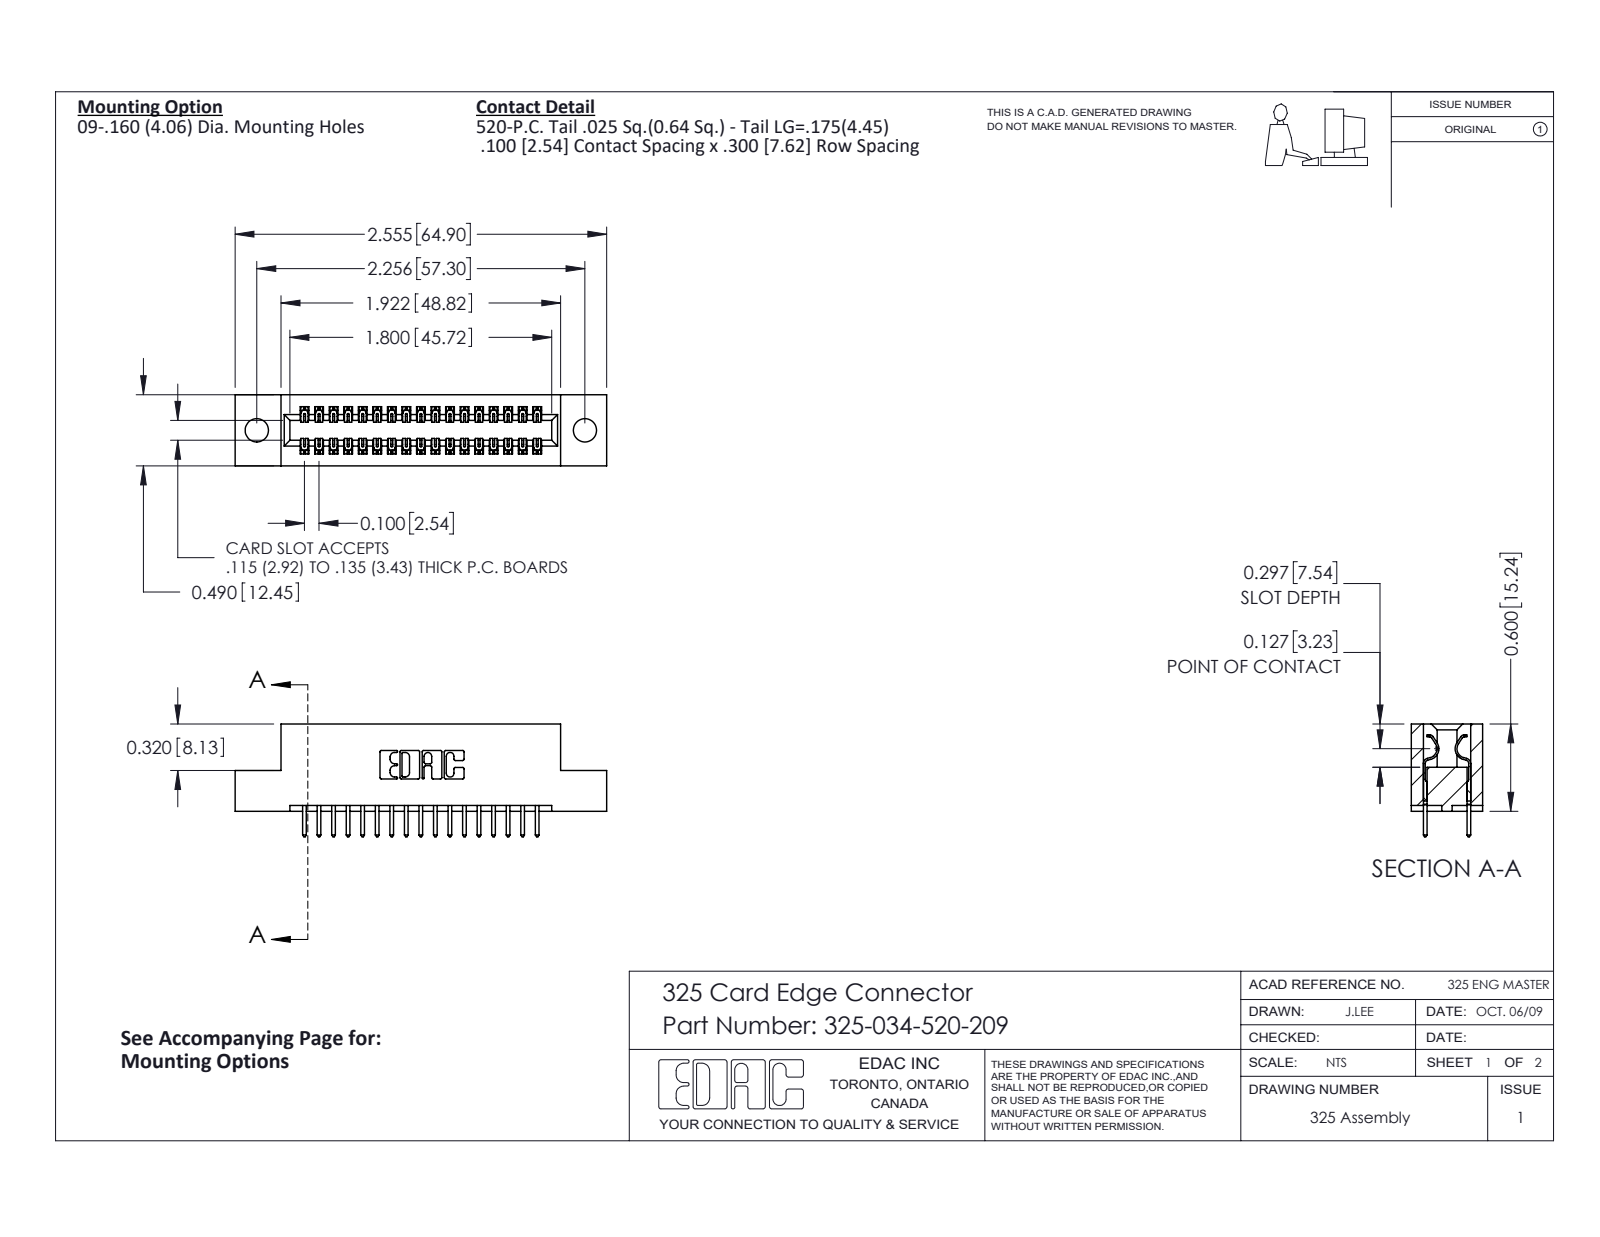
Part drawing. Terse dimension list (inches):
name: 325-292-001_325-293-120; 325 Part_.160 TH; 325-034-520-209
written by: SolidWorks 2016 (CONFIG_CONTROL_DESIGN)
unit: in
bodies: 35 solids, 1882 faces (1294 planar, 588 cylindrical, 0 other)
size: 2.555 × 0.775 × 0.49
volume: 0.483 in³; area: 13.71 in²
holes: 2× ⌀0.16
rounds: 51× R0.006, 34× R0.01, 22× R0.01, 6× R0.007, 6× R0.031, 3× R0.026, 2× R0.014, 2× R0.022
face distances: 0.083, 0.407, 0.3, 0.49, 0.107, 0.383, 0.025, 0.325, 0.6, 0.04
hole spacings: 2.256
